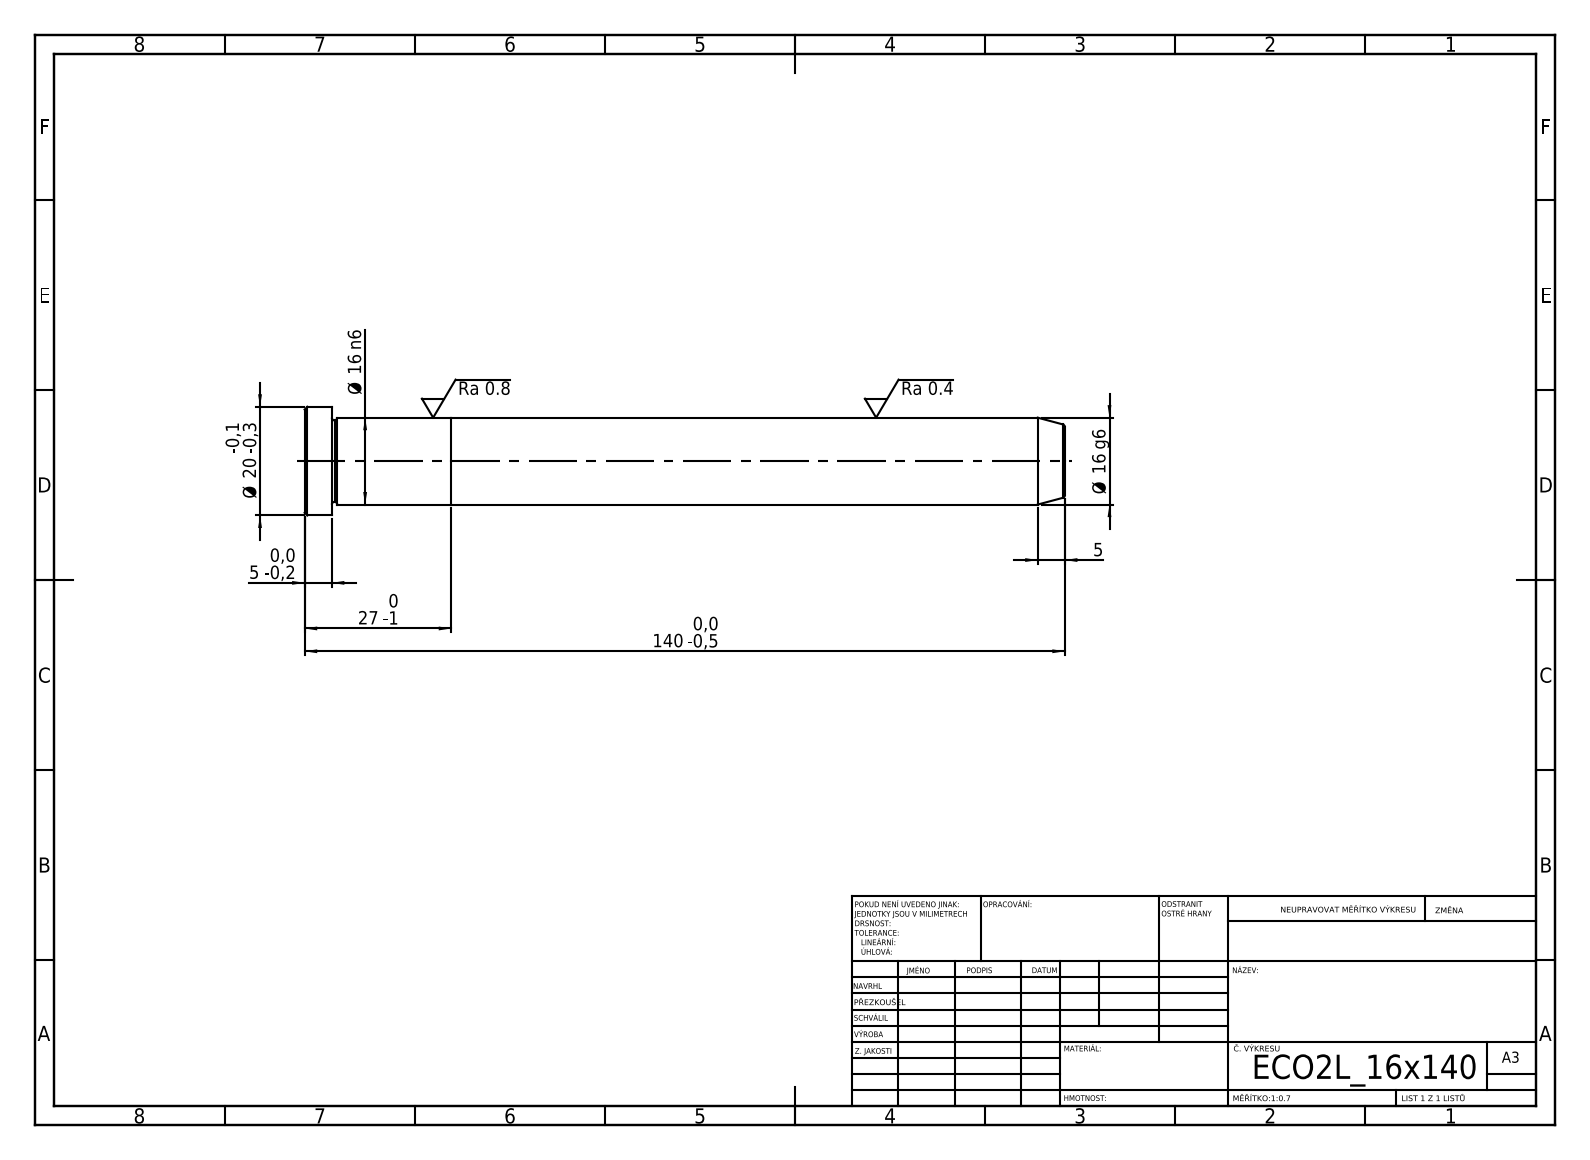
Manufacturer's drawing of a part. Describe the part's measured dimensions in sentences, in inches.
Its 3-D file was written by "SolidWorks 2019 (CONFIG_CONTROL_DESIGN)". It is 2 solids with 21 faces: 5 planar, 6 cylindrical and 10 other. Overall it measures 5.512 by 0.787 by 0.787 inches. Its volume is 1.741 cubic inches and its surface area 12.49 square inches. Round bosses or shafts: 1 of diameter 0.787, 1 of diameter 0.63. The main face-to-face distances are 1.063, 4.449, 5.512, 5.315, 0.866, 0.197.
